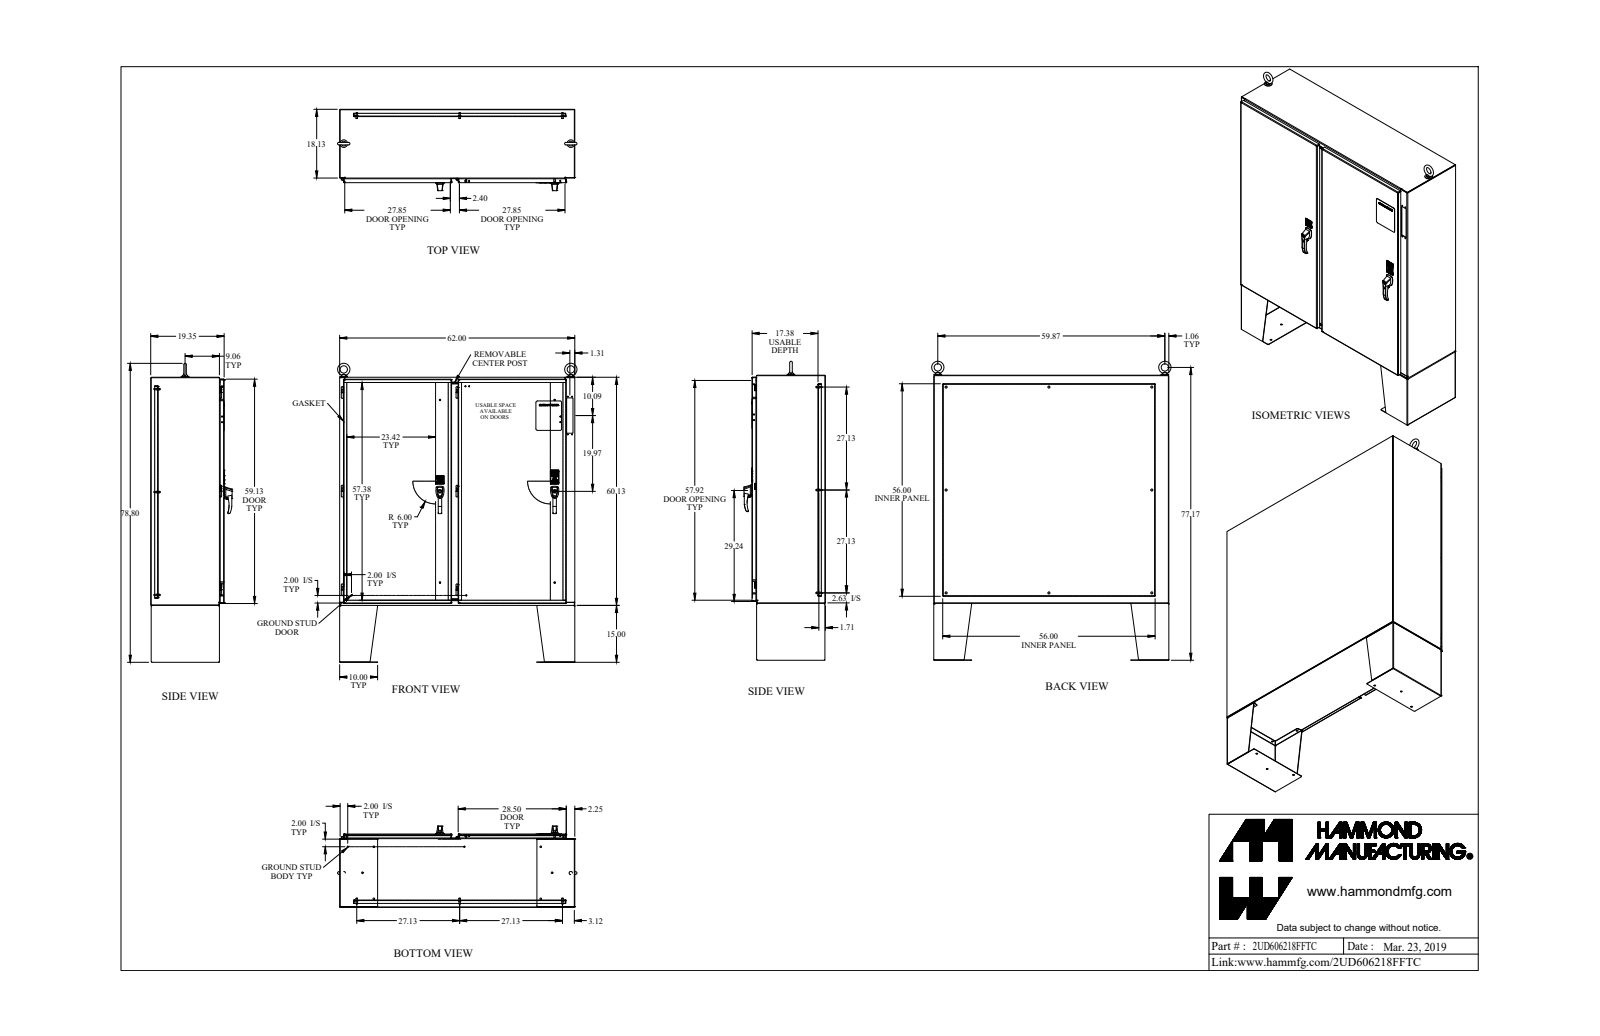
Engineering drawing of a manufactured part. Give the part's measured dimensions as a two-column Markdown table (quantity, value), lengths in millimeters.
| quantity | value |
| --- | --- |
| part name | 2UD606218FFTC |
| STEP written by | SolidWorks 2018 (AUTOMOTIVE_DESIGN) |
| units | millimeters |
| bodies | 214 solids, 3142 faces (1822 planar, 934 cylindrical, 386 other) |
| overall size | 2001.5 × 1603.3 × 545.2 |
| volume | 59 400 000 mm³ |
| surface area | 25 650 000 mm² |
| round holes (diameter × count) | 11.1 × 14, 7.1 × 11, 7.8 × 11, 5 × 10, 6.4 × 10, 8.9 × 8, 6.5 × 6, 8 × 6, 11.3 × 5, 7.1 × 4, 7.2 × 4, 9.5 × 4 |
| round bosses / shafts (diameter × count) | 6.4 × 19, 25.4 × 14, 16.5 × 9, 9.5 × 9, 8.4 × 9, 7.1 × 8, 19.1 × 6, 13.5 × 6 |
| partial cylindrical surfaces (radius × count) | 3.2 × 62, 1.5 × 51, 12.7 × 38, 0.4 × 32, 4.7 × 30, 0.8 × 28, 1.2 × 20, 3.6 × 20 |
| main face-to-face distances | 3.2, 1.8, 442.7, 491.9, 488.8, 49.2, 46, 47.4, 44.2, 444.6 |
| hole center spacings | 25.4, 768.4, 1378, 190.2, 206.4, 220.3, 408.1, 1206.5 |
